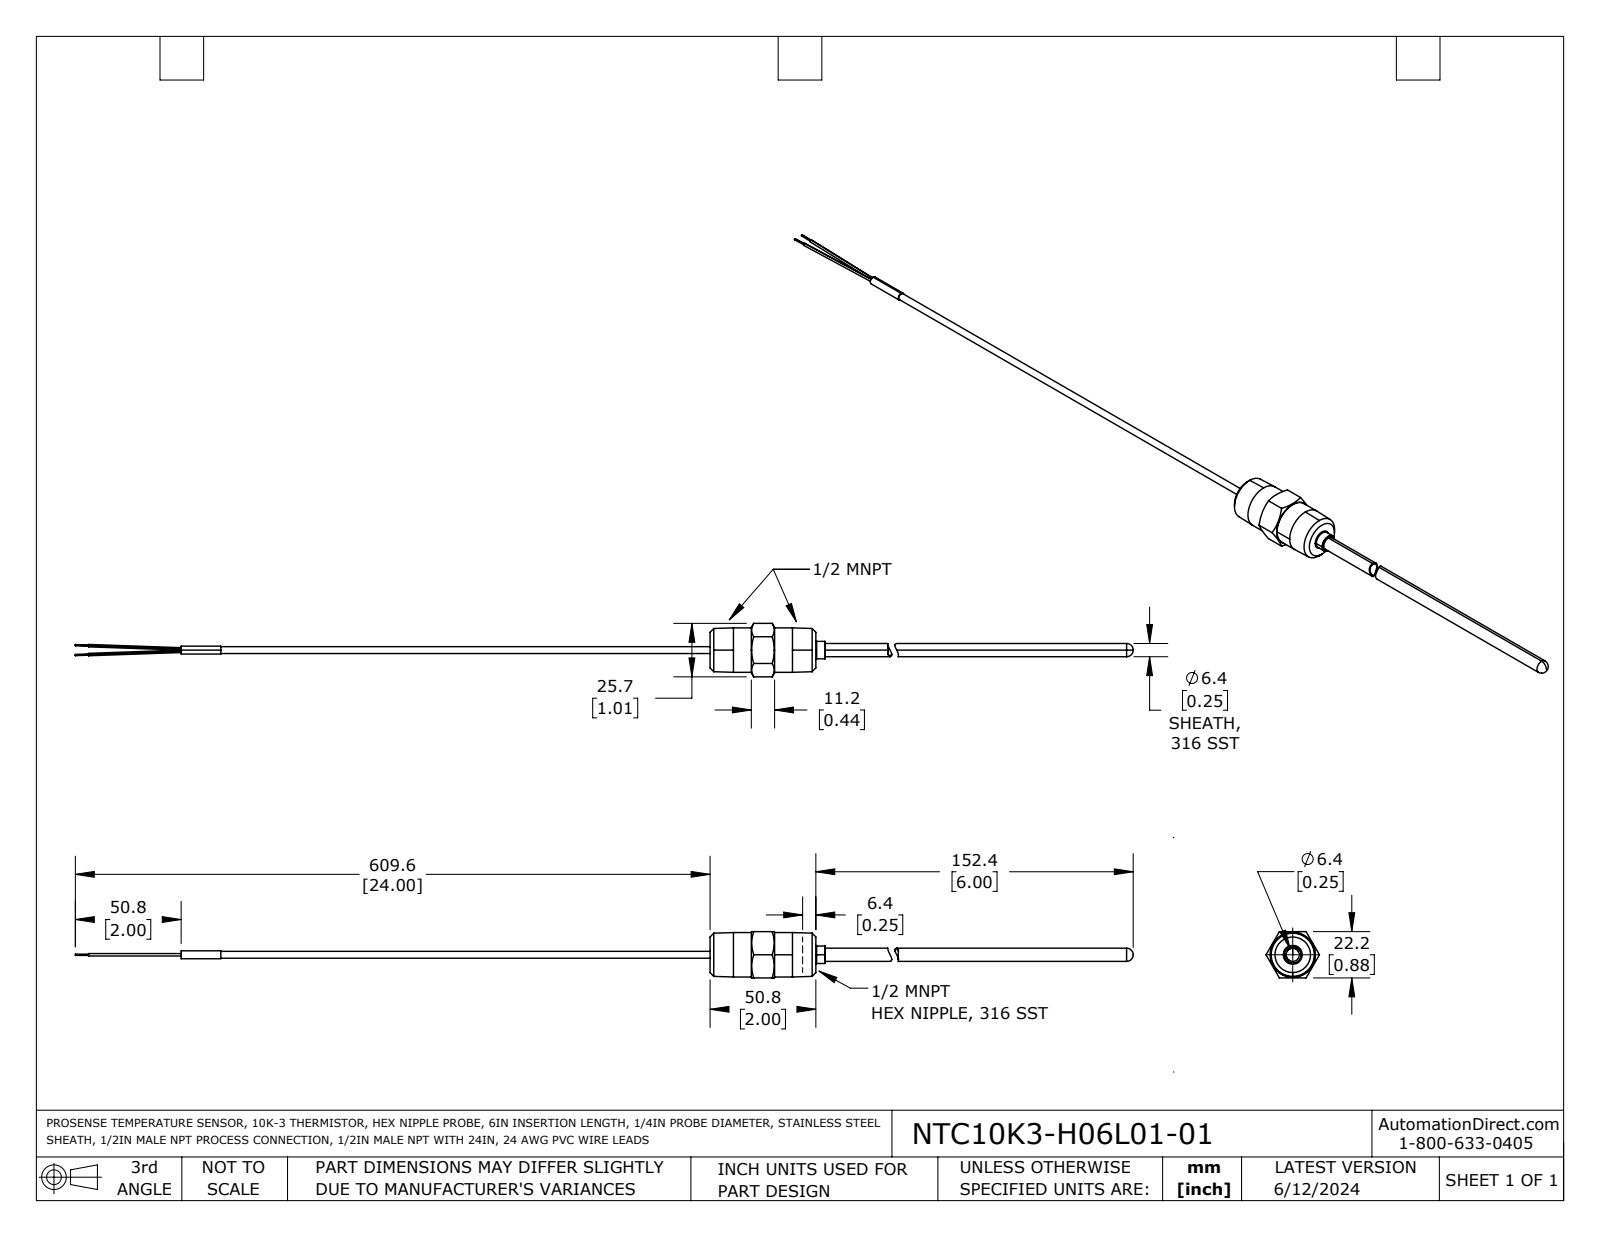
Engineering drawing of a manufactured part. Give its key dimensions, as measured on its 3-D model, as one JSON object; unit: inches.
{"part_name": "NTC10K3-H06L01-01 fxt", "step_written_by": "SolidWorks 2021 (AUTOMOTIVE_DESIGN)", "units": "inches", "bodies": {"solids": 2, "faces": 73, "planar": 23, "cylindrical": 20, "other": 30}, "overall_size": [19.995, 1.01, 0.875], "volume_in3": 1.103, "surface_area_in2": 23.19, "round_holes": [[0.131, 1], [0.21, 1], [0.253, 1], [0.438, 1]], "round_bosses_or_shafts": [[0.84, 1], [0.33, 1], [0.25, 1], [0.15, 1], [0.13, 1]], "face_to_face_distances": [0.875, 2, 0.107, 1.893, 0.1, 1.993, 0.78, 1.22, 7.774, 7.767]}
